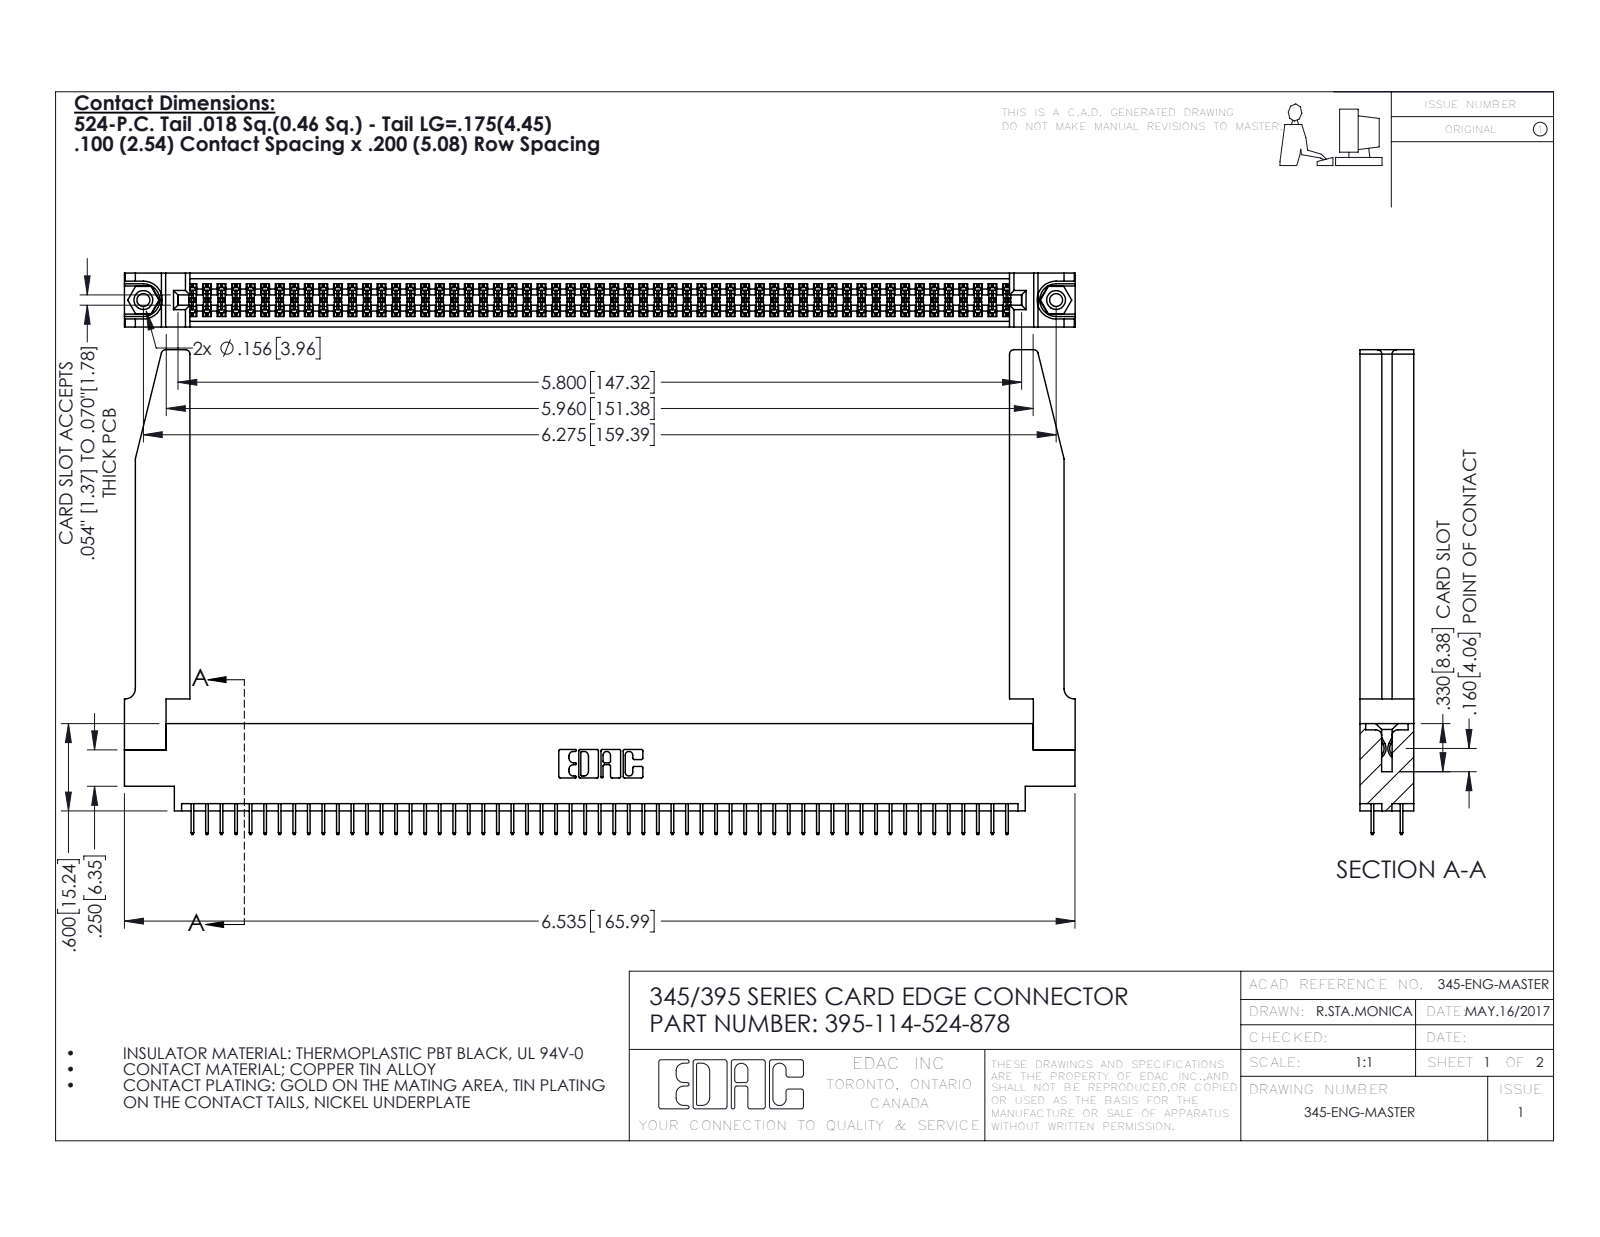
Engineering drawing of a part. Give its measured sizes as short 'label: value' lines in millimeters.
name: 345 Part_0.170 Offset - 0.156 Dia-TH; 345-292-001_345-293-124; 345-250-001_345-250-001-102; 395-114-524-878 (+1 more)
written by: SolidWorks 2016 (CONFIG_CONTROL_DESIGN)
unit: mm
bodies: 119 solids, 6520 faces (4672 planar, 1796 cylindrical, 52 other)
size: 166 × 84.6 × 9.4
volume: 23 740 mm³; area: 30 440 mm²
holes: 2× ⌀2.3, 2× ⌀3.2, 2× ⌀4, 1× ⌀1.6
bosses: 2× ⌀3.9
rounds: 171× R0.2, 22× R0.3, 8× R0.8, 6× R0.2, 6× R0.8, 3× R0.7, 2× R0.4, 2× R0.5
face distances: 9.4, 1.8, 7.6, 5.1, 2.5, 6.9, 0.6, 5.7, 1.8, 4.4
hole spacings: 6.9, 153.4, 159.4
